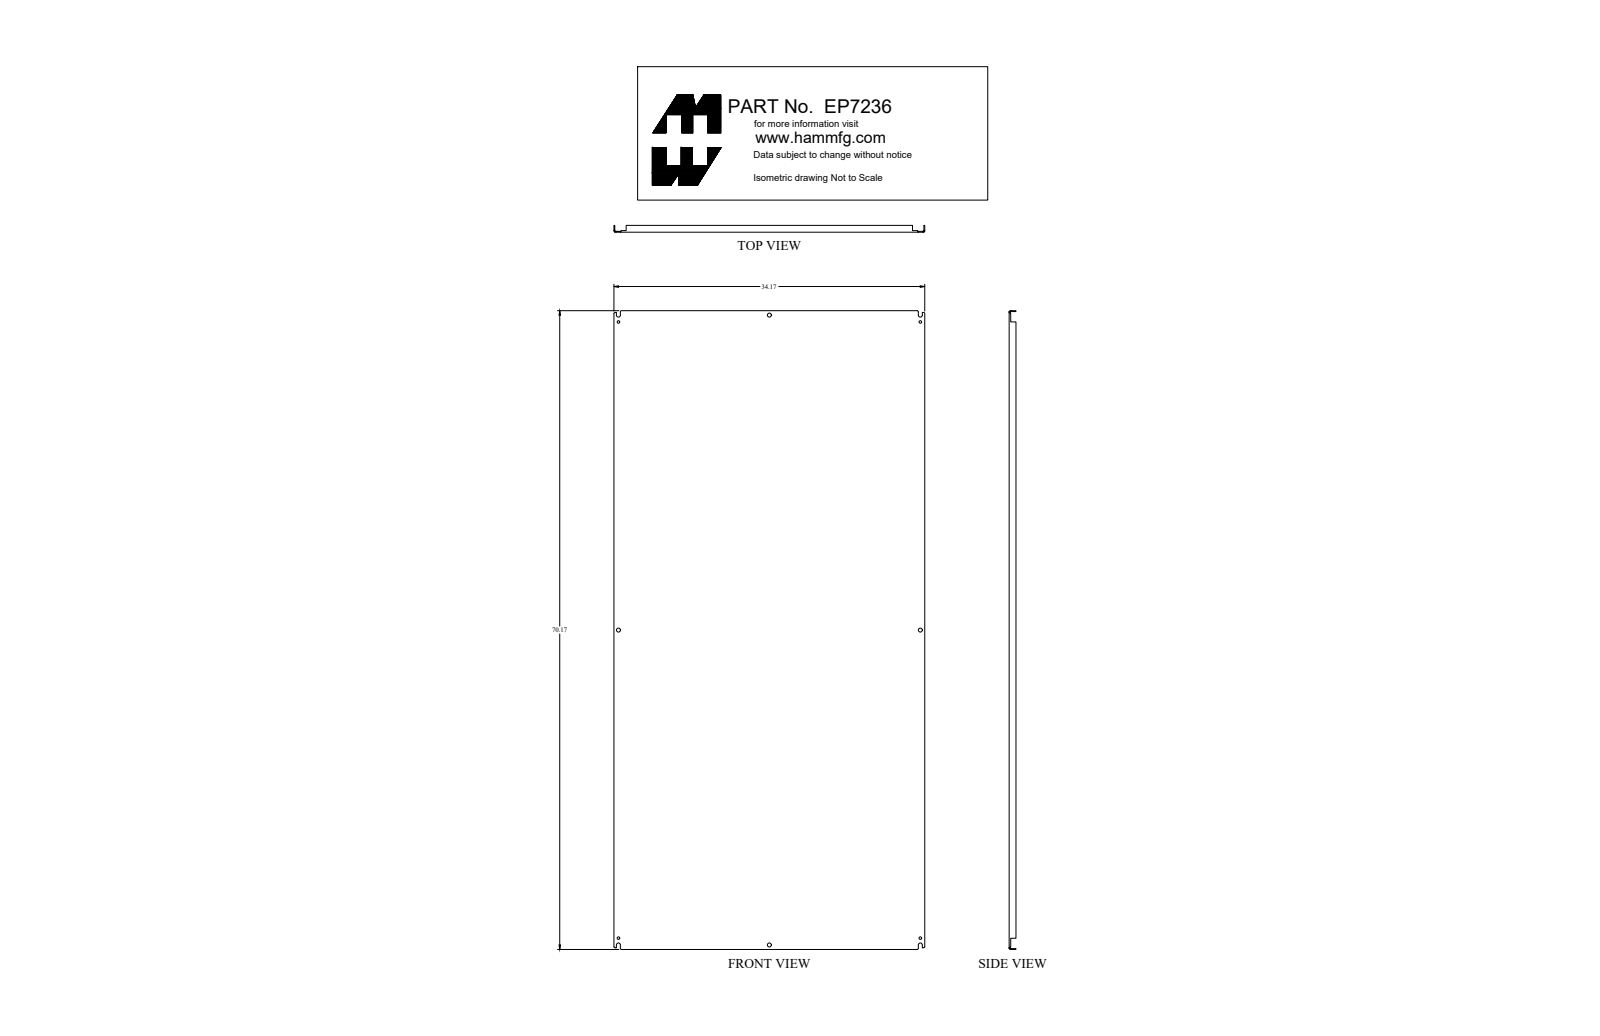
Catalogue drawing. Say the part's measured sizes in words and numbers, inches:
The part is named "EP7236". Its 3-D file was written by "SolidWorks 2018 (AUTOMOTIVE_DESIGN)". It is 1 solid with 136 faces: 74 planar, 46 cylindrical and 16 other. Overall it measures 70.17 by 34.17 by 0.75 inches. Its volume is 239.1 cubic inches and its surface area 5 056 square inches. Round holes: 4 of diameter 0.281, 4 of diameter 0.437. Partial cylindrical surfaces (rounded edges, fillets, slot ends): 4 of radius 0.048, 4 of radius 0.063, 4 of radius 0.143, 4 of radius 0.219. The main face-to-face distances are 0.095, 34.075, 34.17, 33.98, 70.075, 69.98, 70.17, 0.75, 0.655, 0.171. The hole center spacings are 16.611, 33.844, 38.368, 47.401, 70.421, 33.188, 67.688, 75.387.
